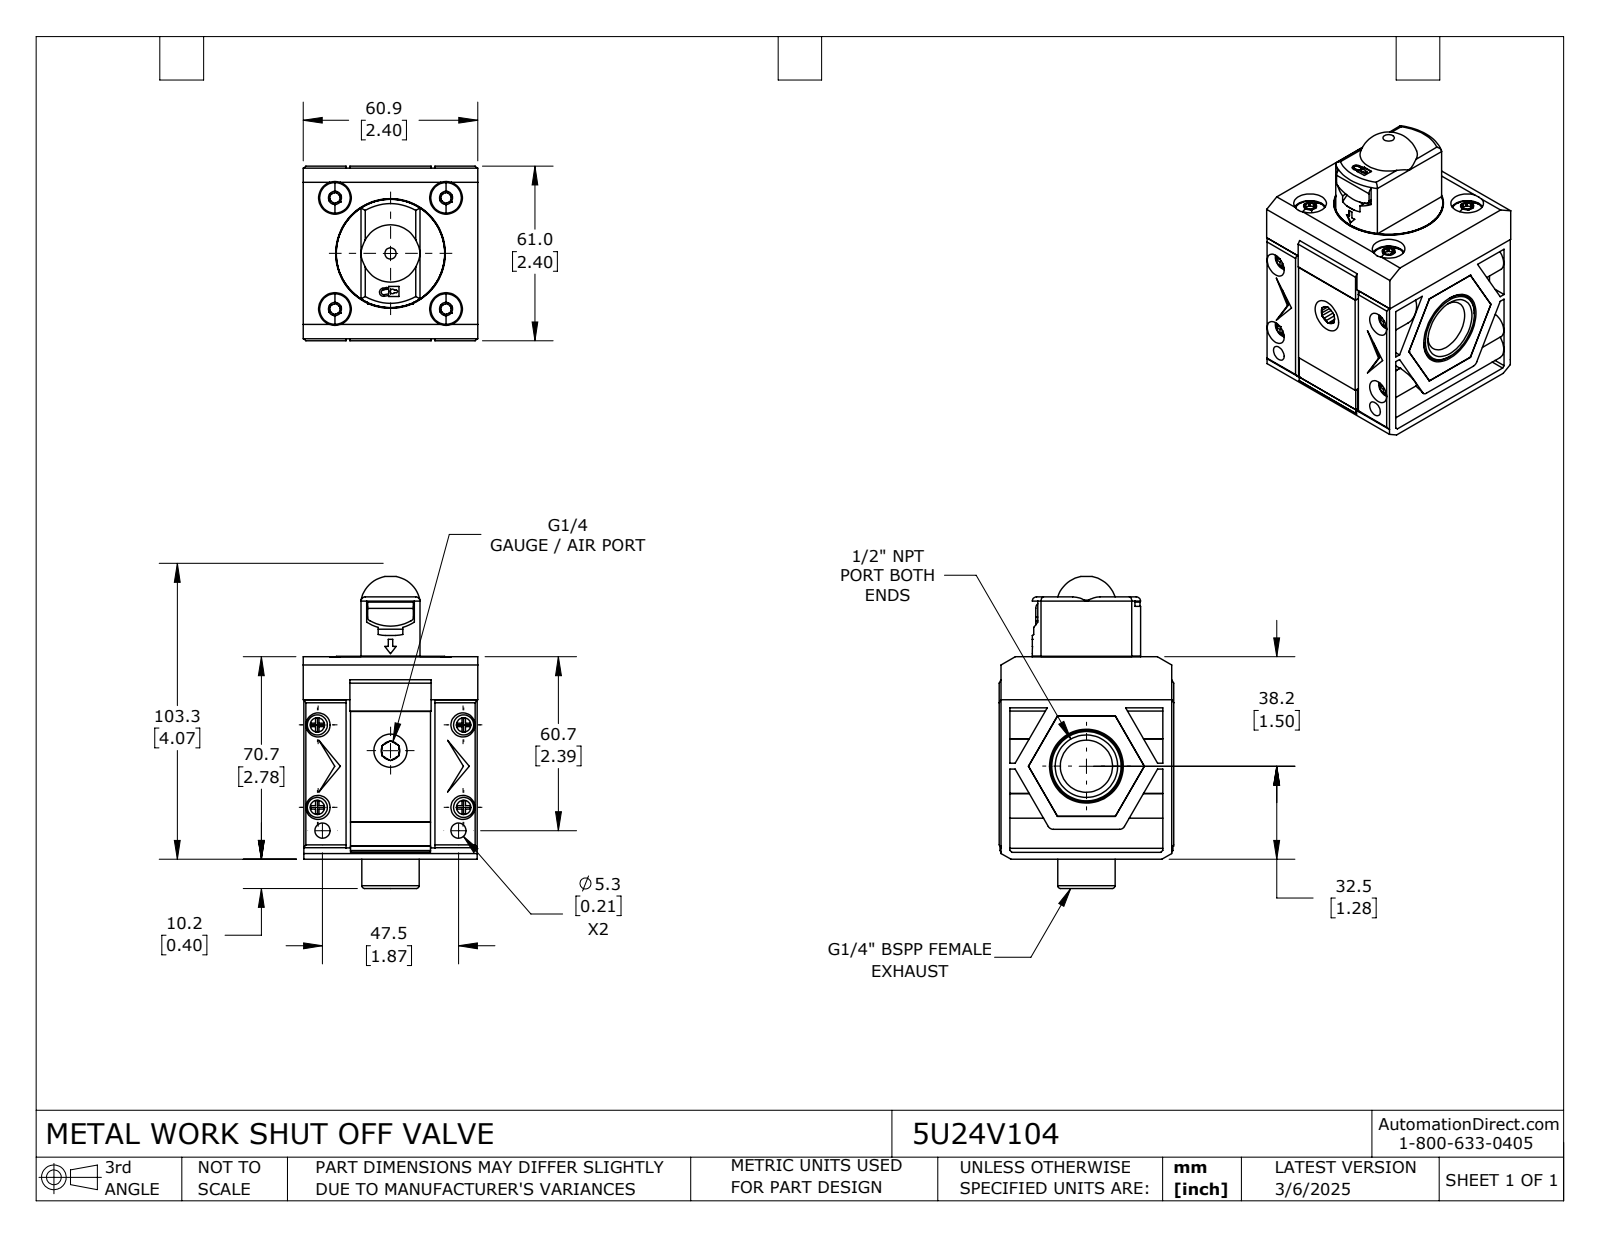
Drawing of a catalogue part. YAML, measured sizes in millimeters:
part_name: "5U24V104"
step_written_by: "SolidWorks 2024 (CONFIG_CONTROL_DESIGN)"
units: millimeters
bodies: {solids: 13, faces: 792, planar: 450, cylindrical: 202, other: 140}
overall_size: [108.91, 61, 60.9]
volume: 247681
surface_area: 70768
round_holes:
  - {diameter: 3.24, count: 4}
  - {diameter: 4.2, count: 4}
  - {diameter: 8.4, count: 4}
  - {diameter: 11.4, count: 4}
  - {diameter: 5.3, count: 2}
  - {diameter: 11.45, count: 1}
  - {diameter: 11.6, count: 1}
  - {diameter: 38.3, count: 1}
round_bosses_or_shafts:
  - {diameter: 7, count: 4}
  - {diameter: 4.8, count: 4}
  - {diameter: 3.8, count: 4}
  - {diameter: 38, count: 1}
  - {diameter: 31.7, count: 1}
  - {diameter: 26.3, count: 1}
  - {diameter: 23.5, count: 1}
  - {diameter: 23.3, count: 1}
partial_cylinders:
  - {radius: 0.28, count: 24}
  - {radius: 1.5, count: 4}
  - {radius: 1.75, count: 4}
  - {radius: 4.85, count: 4}
  - {radius: 2, count: 2}
  - {radius: 6.15, count: 2}
  - {radius: 15, count: 2}
  - {radius: 0.45, count: 1}
face_to_face_distances: [2.4, 60.7, 55.7, 53.3, 7.6, 61, 60.5, 0.7, 45.7, 58.9]
hole_center_spacings: [27.44, 38.8, 8.25, 26.85, 28.8, 32.13, 36.64, 36.93]
